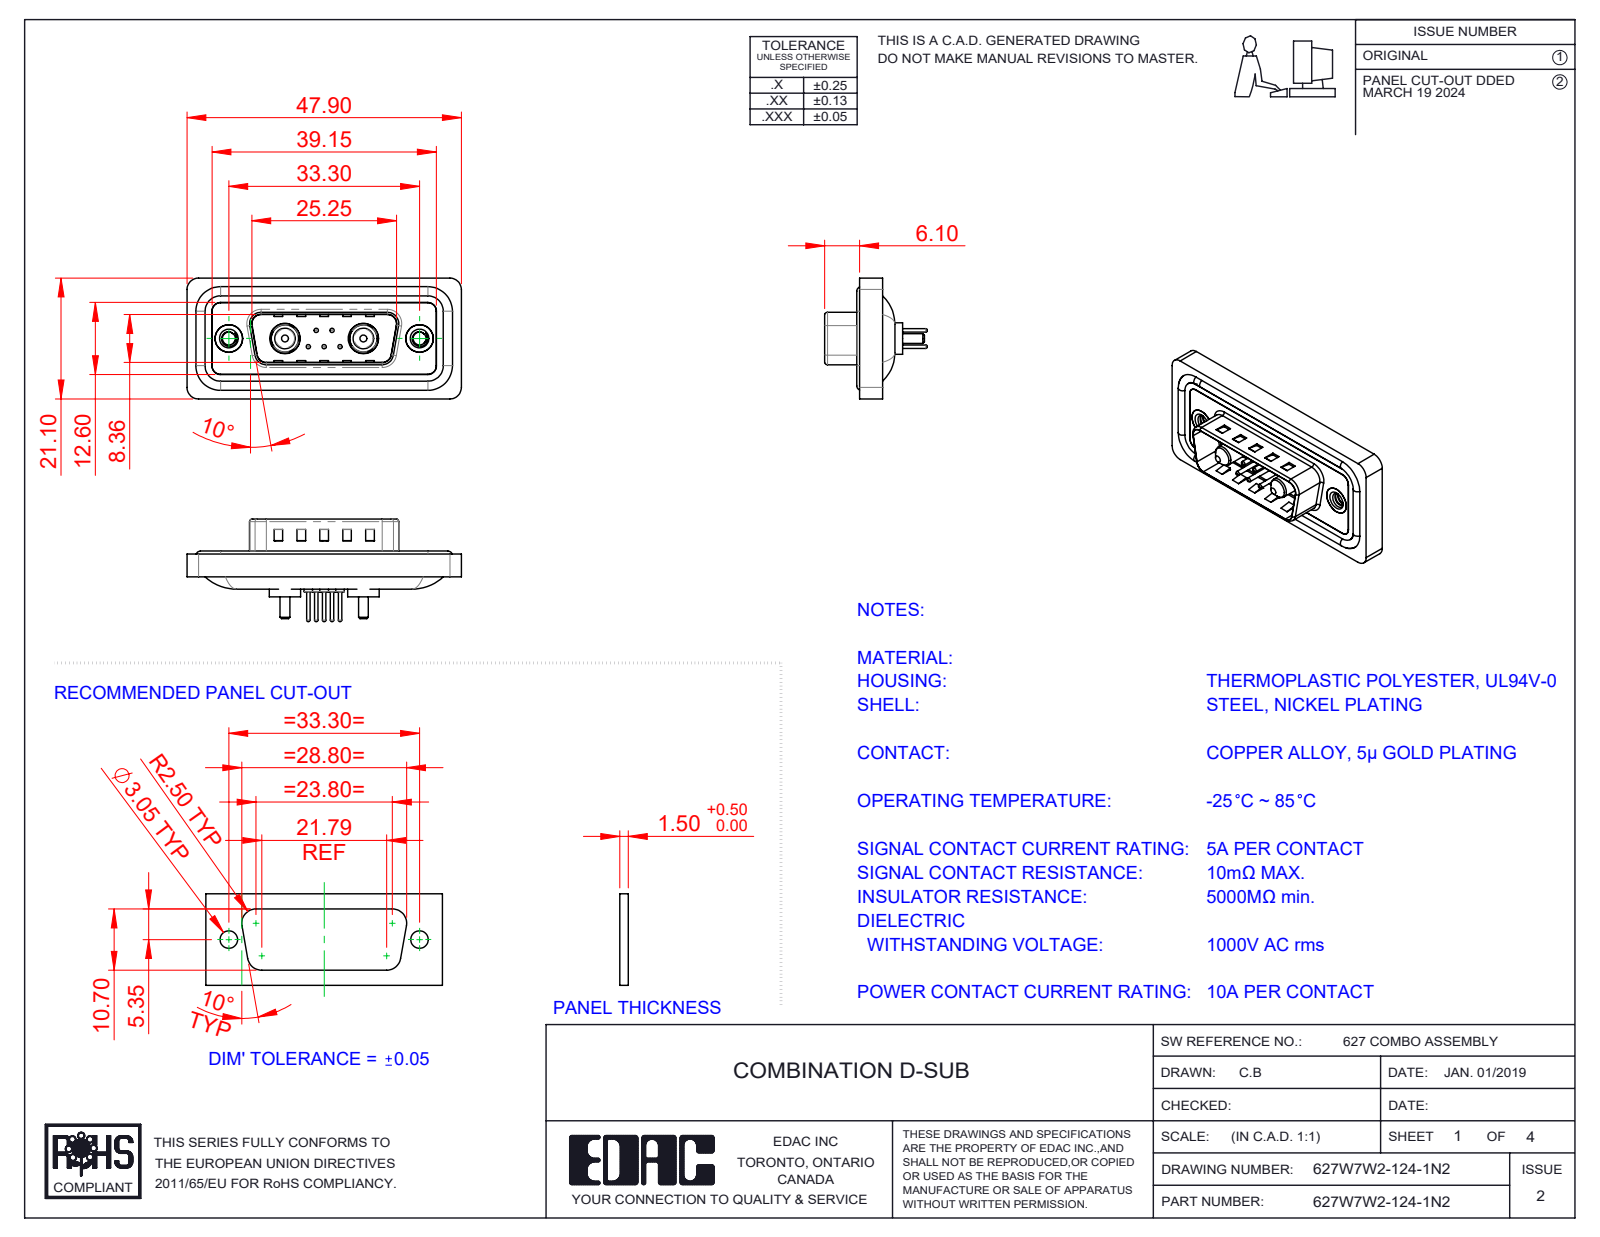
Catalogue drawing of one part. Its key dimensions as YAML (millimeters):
part_name: "627Combo Shell Front_15 Contacts; 627Combo Contact Row 1_24; 627W7W2-124-1N2; 627Combo Threaded Rivet_2 (+5 more)"
step_written_by: "SolidWorks 2023 (CONFIG_CONTROL_DESIGN)"
units: millimeters
bodies: {solids: 16, faces: 710, planar: 232, cylindrical: 292, other: 186}
overall_size: [47.9, 21.1, 17.9]
volume: 5487
surface_area: 8767
round_holes:
  - {diameter: 0.75, count: 5}
  - {diameter: 1.6, count: 5}
  - {diameter: 2, count: 5}
  - {diameter: 2.26, count: 2}
  - {diameter: 4, count: 2}
  - {diameter: 4.8, count: 2}
  - {diameter: 4.85, count: 2}
  - {diameter: 5, count: 2}
  - {diameter: 5.3, count: 2}
round_bosses_or_shafts:
  - {diameter: 1.5, count: 5}
  - {diameter: 0.6, count: 5}
  - {diameter: 1.6, count: 4}
  - {diameter: 5.5, count: 2}
  - {diameter: 5.2, count: 2}
  - {diameter: 4.9, count: 2}
  - {diameter: 4.75, count: 2}
  - {diameter: 3.75, count: 2}
partial_cylinders:
  - {radius: 1.5, count: 26}
  - {radius: 2, count: 20}
  - {radius: 0.5, count: 8}
  - {radius: 1.6, count: 8}
  - {radius: 0.25, count: 4}
  - {radius: 0.6, count: 4}
  - {radius: 0.65, count: 4}
  - {radius: 0.9, count: 4}
face_to_face_distances: [0.4, 1.1, 1.5, 1.6, 0.5, 3.1, 2.9, 4, 0.82, 9.58]
hole_center_spacings: [3.16, 2.77, 9.8, 23.5, 4.31, 4.33, 5.03, 5.04]
